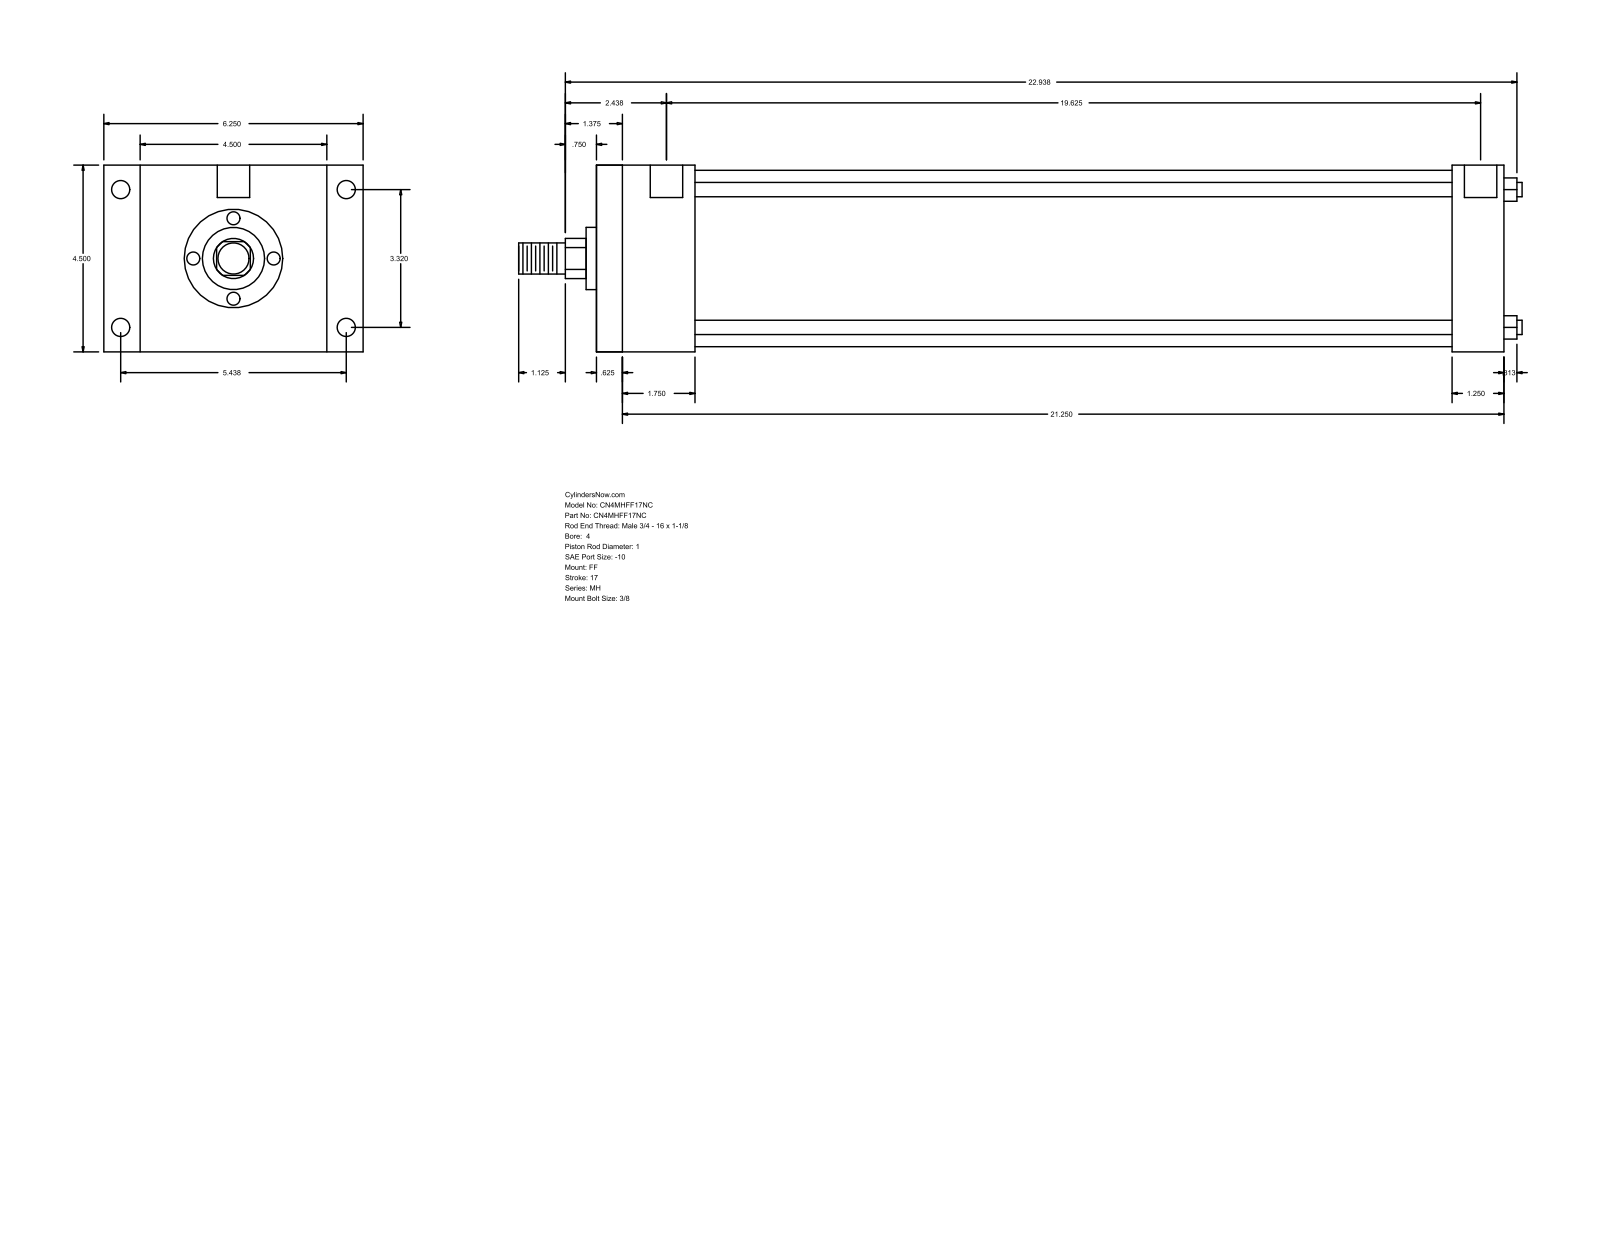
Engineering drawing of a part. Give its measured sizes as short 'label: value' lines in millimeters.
name: MH_FF__0400_1
written by: GSSL Pune (CONFIG_CONTROL_DESIGN)
unit: mm
bodies: 0 solids, 92 faces (64 planar, 28 cylindrical, 0 other)
size: 614.36 × 158.75 × 114.3
holes: 4× ⌀8.73, 4× ⌀11.13, 2× ⌀19.84
bosses: 4× ⌀8.76, 1× ⌀107.95, 1× ⌀38.1, 1× ⌀25.4, 1× ⌀19.05
rounds: 1× R12.29
face distances: 114.3, 555.62, 15.87, 539.75, 60.33, 44.46, 495.29, 523.87, 508, 463.54
hole spacings: 84.32, 138.12, 161.82, 501.65, 1.58, 1.59, 498.48, 500.06
